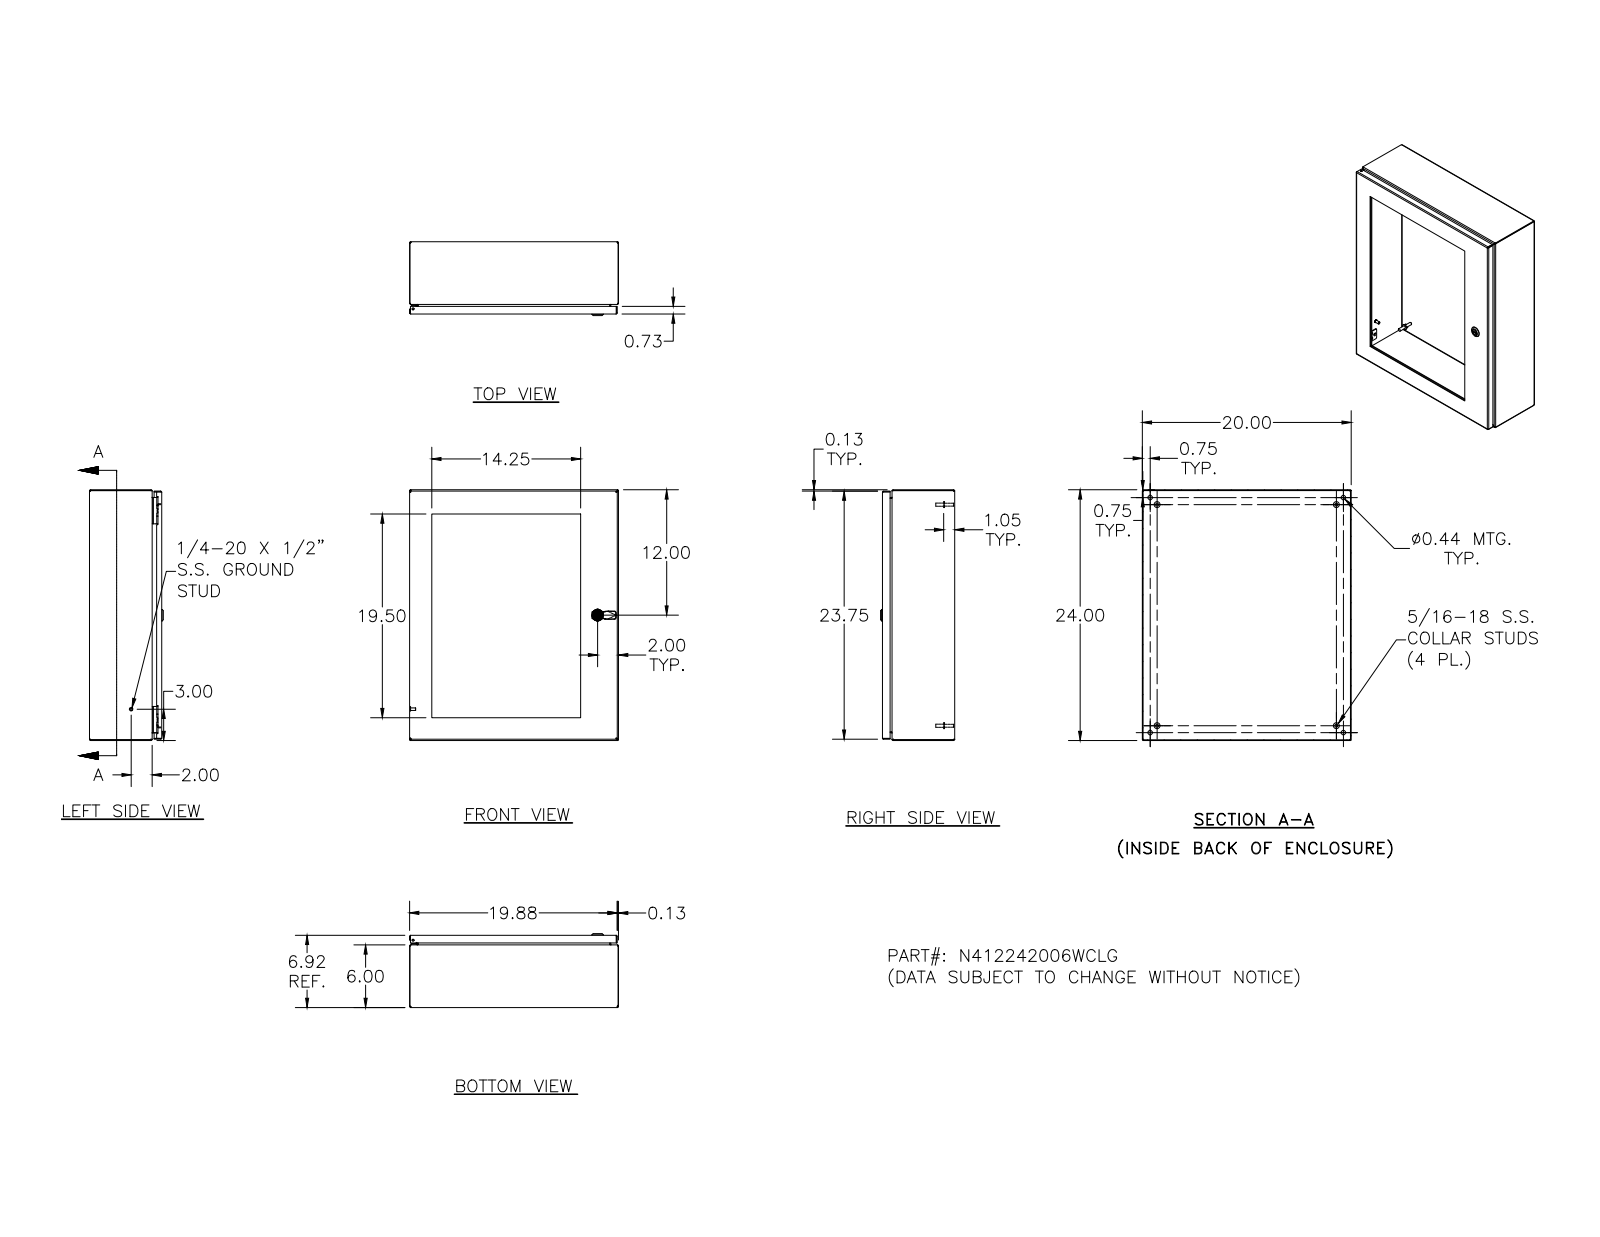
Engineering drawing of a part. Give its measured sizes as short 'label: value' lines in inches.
name: N412242006WCLG
written by: SolidWorks 2018 (AUTOMOTIVE_DESIGN)
unit: in
bodies: 73 solids, 2083 faces (775 planar, 625 cylindrical, 683 other)
size: 24 × 20 × 7.075
volume: 186.9 in³; area: 3 621 in²
holes: 20× ⌀0.156, 18× ⌀0.281, 5× ⌀0.188, 4× ⌀0.093, 4× ⌀0.152, 4× ⌀0.167, 4× ⌀0.172, 4× ⌀0.437, 1× ⌀0.187, 1× ⌀0.197, 1× ⌀0.315, 1× ⌀0.394
bosses: 18× ⌀0.337, 18× ⌀0.19, 10× ⌀0.25, 4× ⌀0.563, 4× ⌀0.36, 4× ⌀0.32, 4× ⌀0.3, 4× ⌀0.275
rounds: 34× R0.031, 30× R0.012, 26× R0.05, 24× R0.105, 18× R0.016, 16× R0.125, 13× R0.02, 8× R0.032
face distances: 0.074, 6.843, 6.769, 0.25, 6.593, 6.519, 19.926, 23.926, 6.917, 0.324
hole spacings: 4, 8, 16.008, 12, 17.443, 20, 21.132, 15.5
